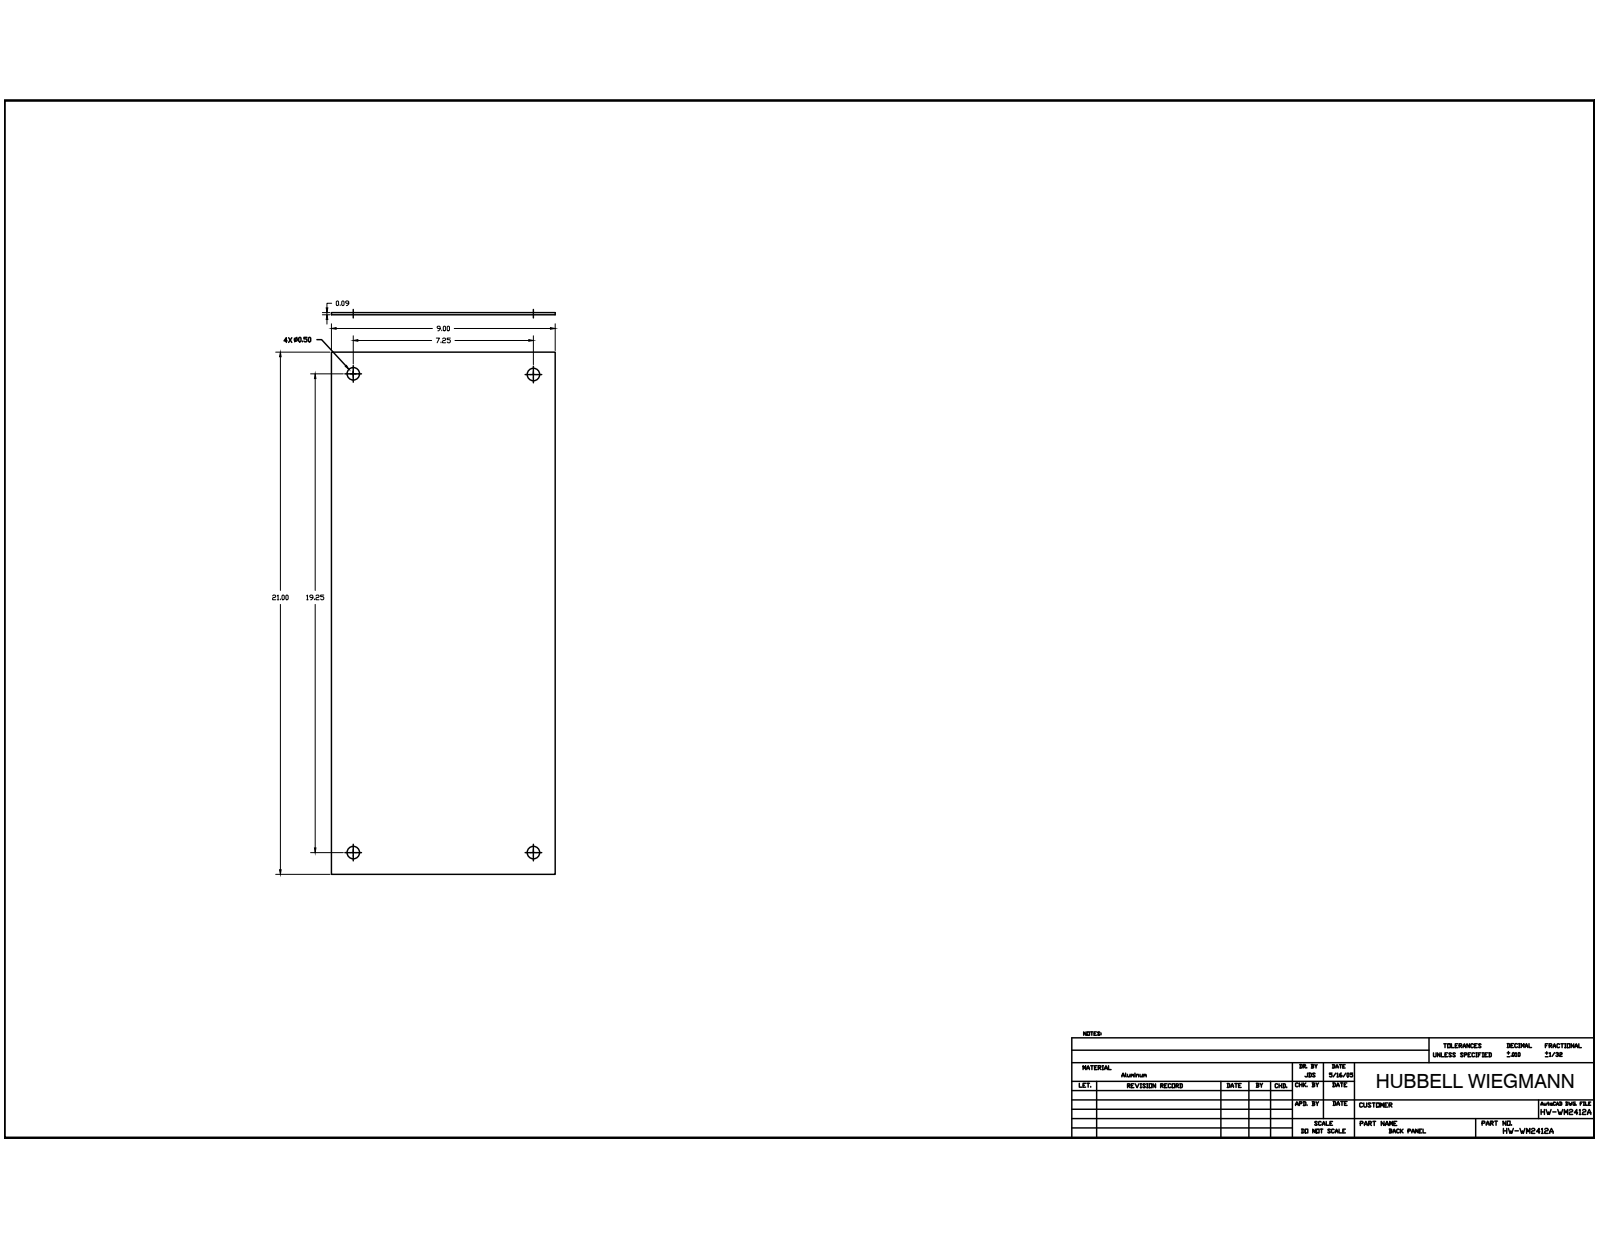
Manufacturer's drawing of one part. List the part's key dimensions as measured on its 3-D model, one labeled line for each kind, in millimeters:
Part name (STEP PRODUCT): BP2412AL_STP
STEP written by: Autodesk Inventor 2014 (AUTOMOTIVE_DESIGN)
Units: millimetres
Bodies: 1 solid, 10 faces (6 planar, 4 cylindrical, 0 other)
Overall size (bounding box): 533.4 × 228.6 × 2.29
Volume: 277 586 mm³ · Surface area: 246 706 mm²
Round holes (diameter × count): ⌀12.7 ×4
Main face-to-face distances: 2.28, 228.6, 533.4
Hole centre spacings: 184.14, 488.95, 522.47
